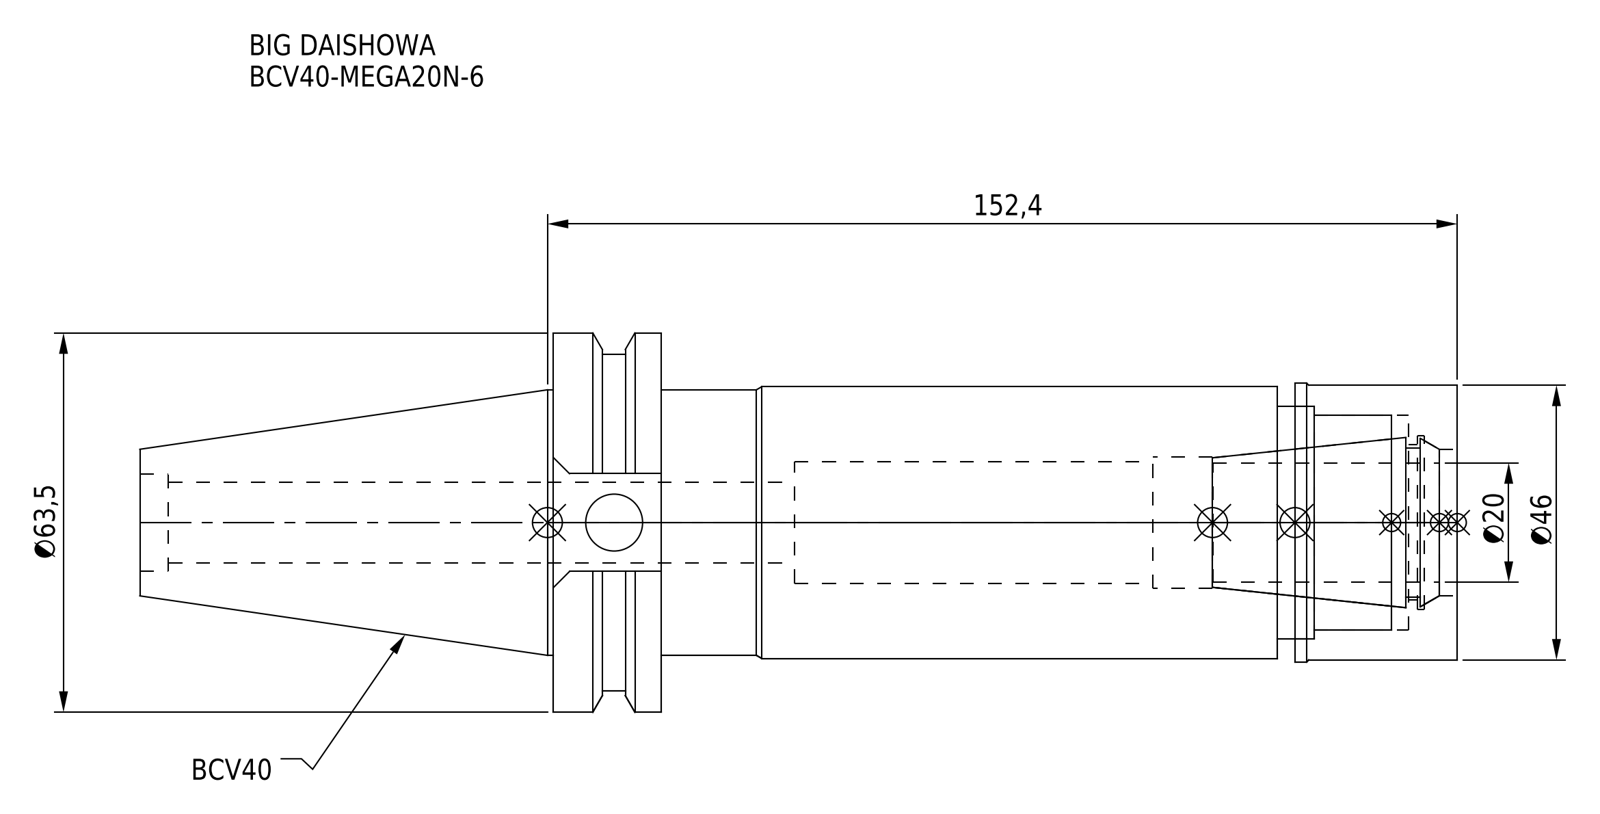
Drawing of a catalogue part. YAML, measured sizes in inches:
part_name: "MGN20_1.stp; BCV40-MEGA20N-6_1.stp; BCV40-MEGA20N-6-200.stp; BCV40MN20060-200_ASM.stp (+3 more)"
step_written_by: "SolidWorks 2019 (CONFIG_CONTROL_DESIGN)"
units: inches
bodies: {solids: 2, faces: 87, planar: 31, cylindrical: 42, other: 14}
overall_size: [8.687, 2.5, 2.415]
volume: 16.53
surface_area: 84.44
round_holes:
  - {diameter: 0.375, count: 1}
  - {diameter: 0.535, count: 1}
  - {diameter: 0.643, count: 1}
  - {diameter: 0.799, count: 1}
  - {diameter: 0.866, count: 1}
  - {diameter: 0.965, count: 1}
  - {diameter: 1.024, count: 1}
  - {diameter: 1.142, count: 1}
  - {diameter: 1.417, count: 1}
  - {diameter: 1.535, count: 1}
round_bosses_or_shafts:
  - {diameter: 2.5, count: 1}
  - {diameter: 2.219, count: 1}
  - {diameter: 1.839, count: 1}
  - {diameter: 1.811, count: 1}
  - {diameter: 1.791, count: 1}
  - {diameter: 1.75, count: 1}
face_to_face_distances: [0.711, 5.25, 5.961, 1.071, 4.179, 4.89, 0.323, 0.748, 4.927, 5.638]
